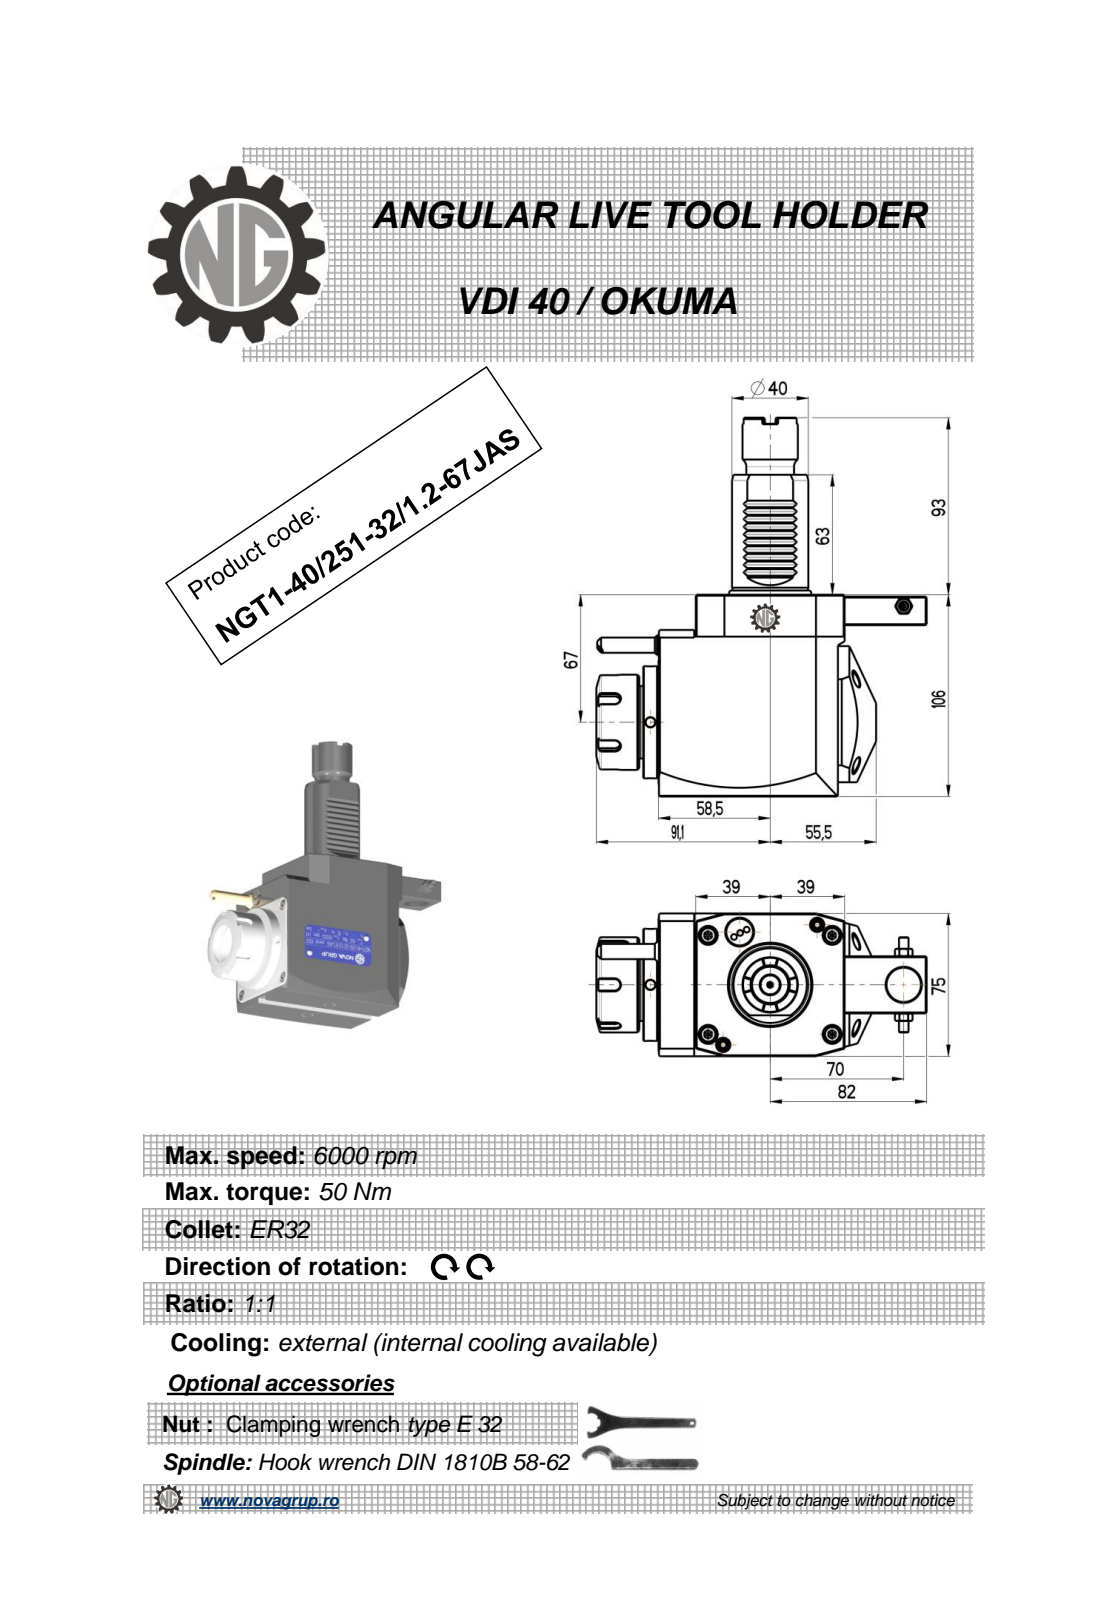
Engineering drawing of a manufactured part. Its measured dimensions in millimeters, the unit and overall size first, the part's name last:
Units: millimetres
Overall size (bounding box): 199 × 173.1 × 75
Round holes (diameter × count): ⌀5 ×3, ⌀3 ×1, ⌀4.2 ×1, ⌀9.5 ×1, ⌀18 ×1, ⌀27 ×1
Round bosses / shafts (diameter × count): ⌀59 ×1, ⌀50 ×1, ⌀47 ×1, ⌀41 ×1, ⌀40 ×1, ⌀29 ×1, ⌀25 ×1, ⌀10 ×1
Partial cylindrical surfaces — rounded edges, fillets, slot ends (radius × count): R0.26 ×12, R0.3 ×10, R0.2 ×6, R3 ×5, R6 ×3, R5.8 ×2, R600 ×2, R10 ×1
Main face-to-face distances: 75, 106, 102, 20, 3.5, 1, 97.5, 19.5, 8, 22.5
Hole centre spacings: 25.83, 44.12, 59.5, 132.75, 146.09
Volume: 941 068 mm³ · Surface area: 78 716 mm²
Bodies: 1 solid, 496 faces (224 planar, 99 cylindrical, 173 other)
Part name (STEP PRODUCT): NGT1_40_251_32_1_2_67JAS
STEP written by: PRO/ENGINEER BY PARAMETRIC TECHNOLOGY CORPORATION, 2010280 (CONFIG_CONTROL_DESIGN)
